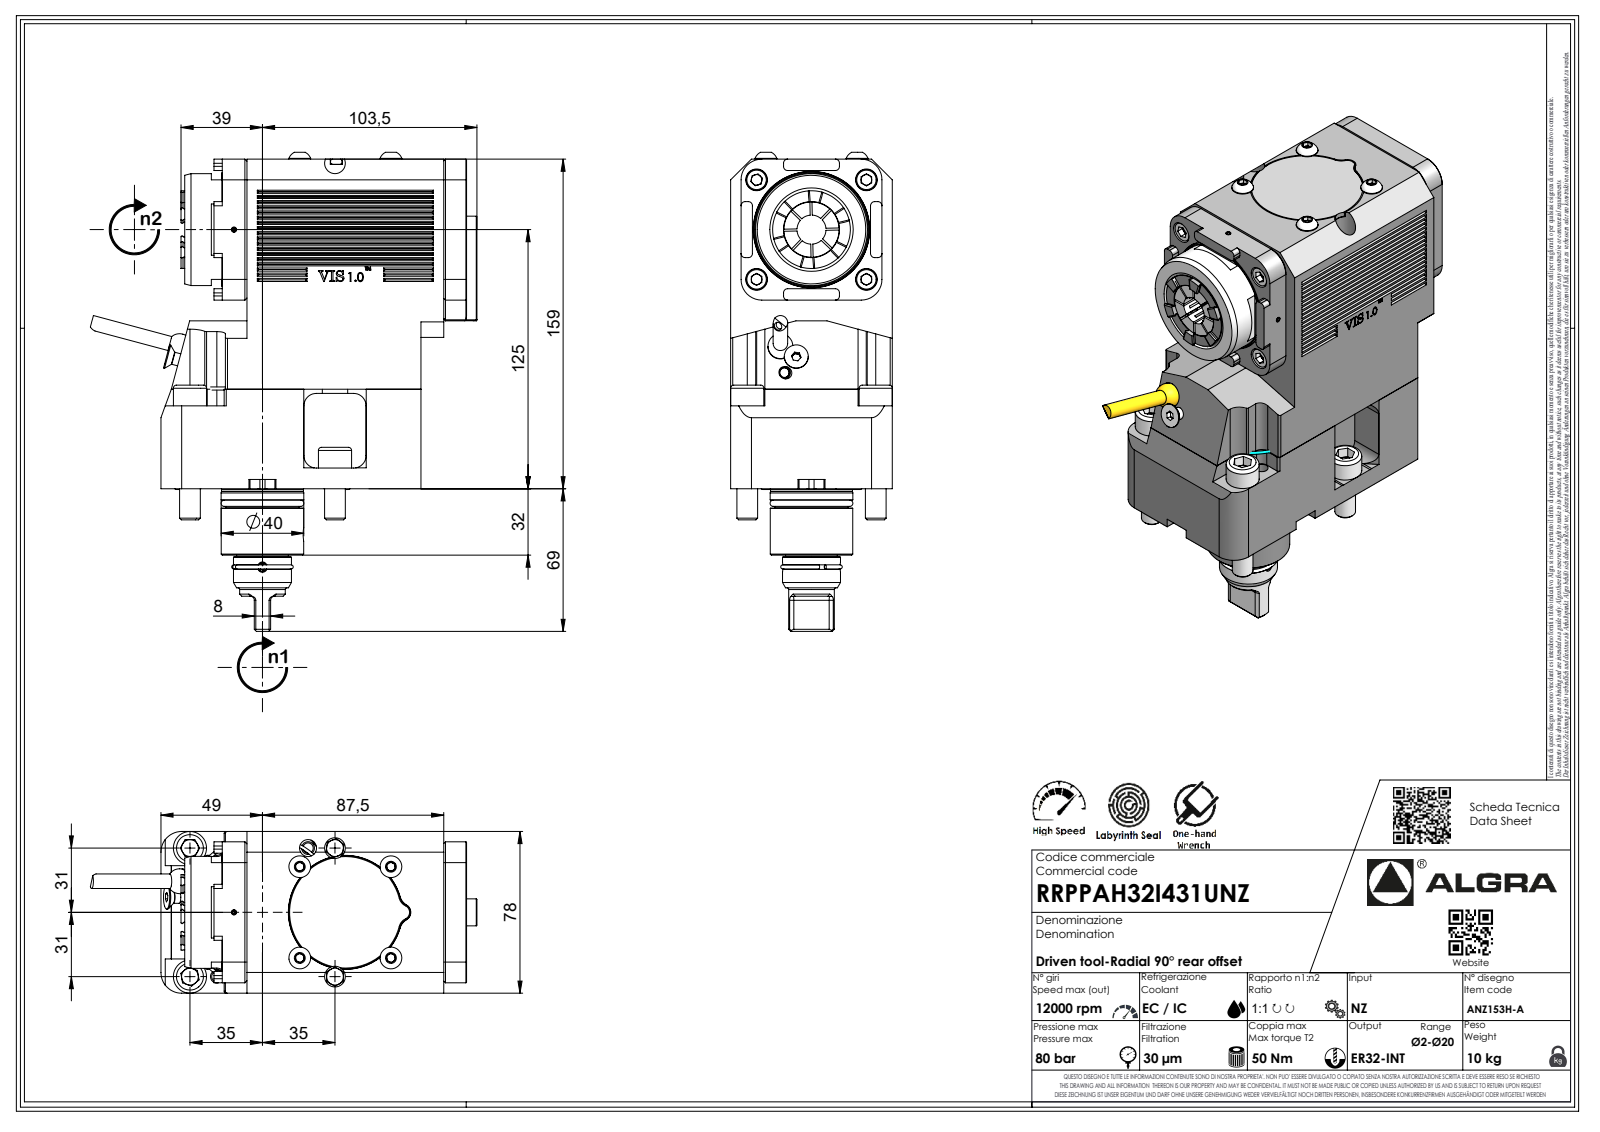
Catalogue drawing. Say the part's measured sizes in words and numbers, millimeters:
The part is named "RRPPAH32I431UNZ". Its 3-D file was written by "SolidWorks 2023 (AUTOMOTIVE_DESIGN)". It is 1 solid with 642 faces: 393 planar, 128 cylindrical and 121 other. Overall it measures 231.1 by 186.57 by 78 millimeters. Its volume is 1 486 000 cubic millimeters and its surface area 105 981 square millimeters. Round holes: 1 of diameter 2.1, 1 of diameter 4. Round bosses or shafts: 4 of diameter 16, 4 of diameter 10.5, 4 of diameter 10, 1 of diameter 54, 1 of diameter 39.9, 1 of diameter 39.8, 1 of diameter 39.5, 1 of diameter 35.1. Partial cylindrical surfaces (rounded edges, fillets, slot ends): 23 of radius 2, 16 of radius 5, 8 of radius 1, 8 of radius 10, 7 of radius 0.33, 7 of radius 0.52, 7 of radius 3.7, 4 of radius 6. The main face-to-face distances are 78, 159, 11.5, 11, 22, 56.5, 5, 30, 73, 16.5.
